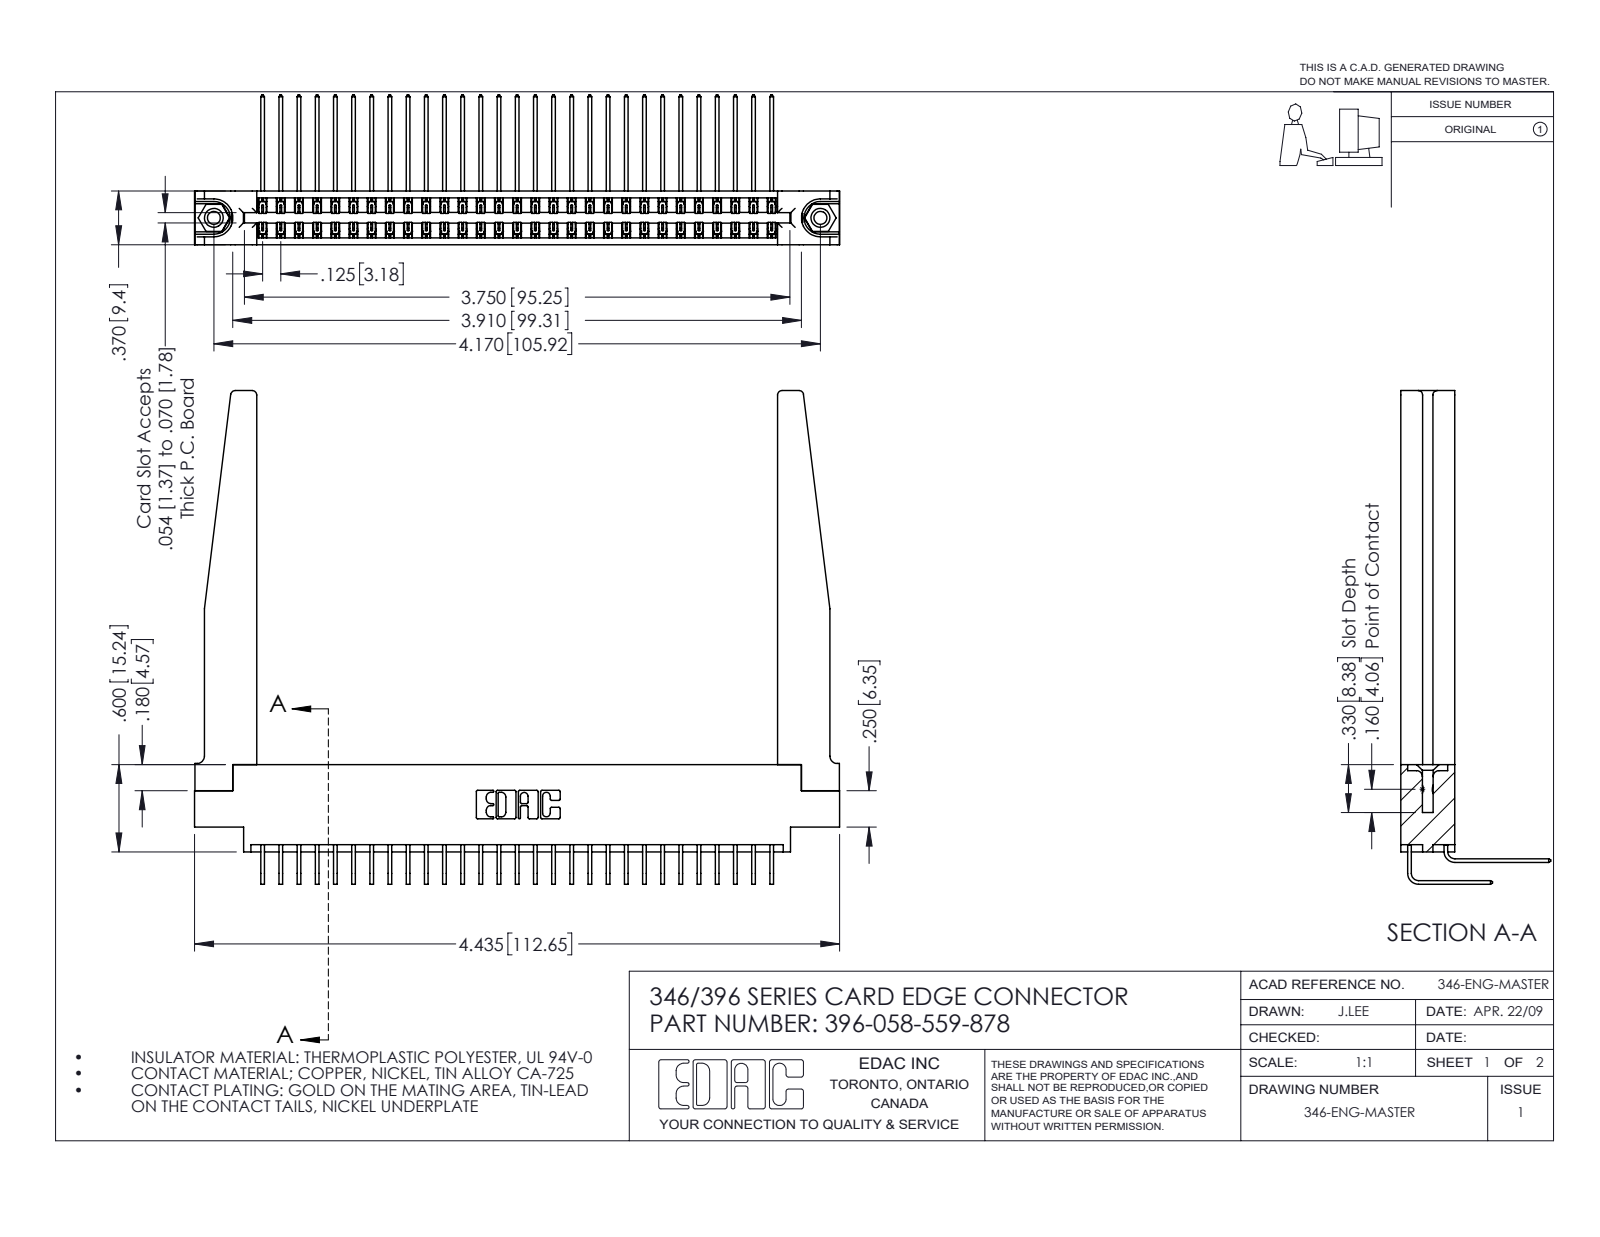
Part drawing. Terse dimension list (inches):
name: 396-058-559-878; 345-250-001_345-250-001-102; 346-220-078_345-220-078; 345-292-001_558 559 Tail - 1 (+2 more)
written by: SolidWorks 2016 (CONFIG_CONTROL_DESIGN)
unit: in
bodies: 63 solids, 3492 faces (2368 planar, 1072 cylindrical, 52 other)
size: 4.435 × 3.393 × 1.03
volume: 1.097 in³; area: 36.15 in²
holes: 2× ⌀0.089, 2× ⌀0.125, 2× ⌀0.156, 1× ⌀0.064
bosses: 2× ⌀0.155
rounds: 87× R0.006, 22× R0.01, 8× R0.03, 6× R0.007, 6× R0.031, 4× R0.05, 3× R0.026, 2× R0.014
face distances: 0.37, 0.048, 0.322, 0.072, 0.025, 0.15, 0.148, 0.25, 0.298, 0.275
hole spacings: 0.246, 3.962, 4.17
